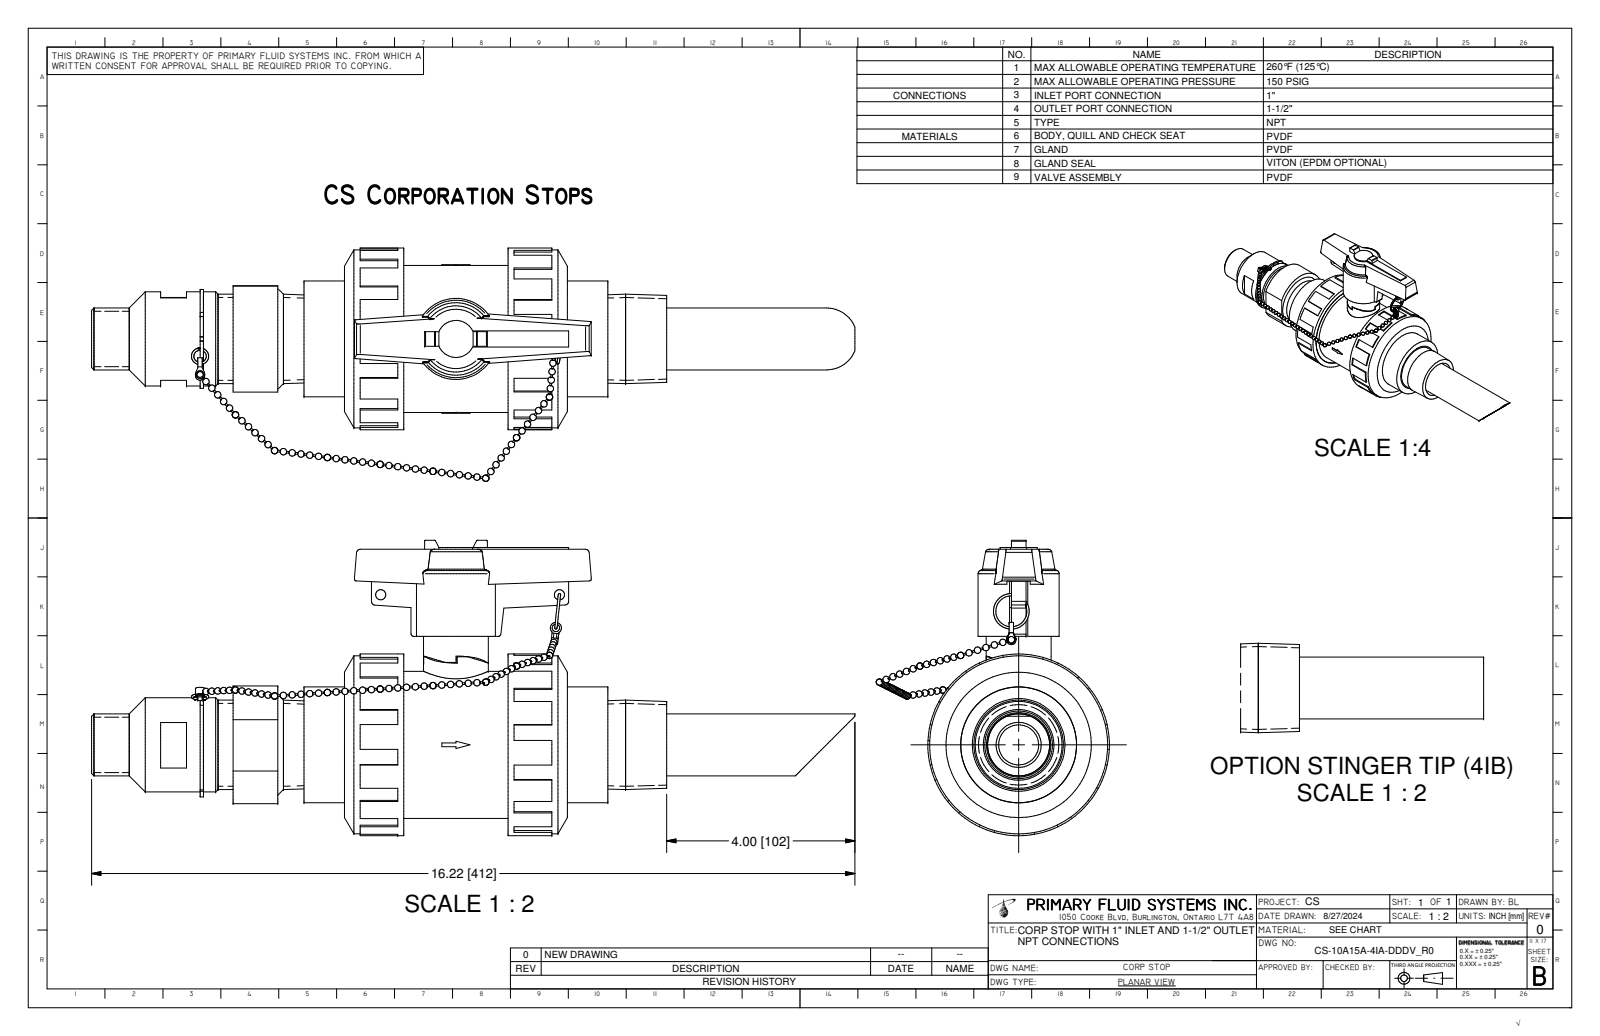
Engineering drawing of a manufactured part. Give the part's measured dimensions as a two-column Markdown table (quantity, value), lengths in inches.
| quantity | value |
| --- | --- |
| STEP written by | Autodesk Inventor 2025 (CONFIG_CONTROL_DESIGN) |
| units | inches |
| bodies | 19 solids, 534 faces (302 planar, 134 cylindrical, 98 other) |
| overall size | 16.221 × 6.274 × 4.956 |
| volume | 63.67 in³ |
| surface area | 403.6 in² |
| round holes (diameter × count) | 0.098 × 2, 0.15 × 2, 0.157 × 2, 0.217 × 2, 0.85 × 1, 0.957 × 1, 1.367 × 1, 1.5 × 1, 1.575 × 1, 1.803 × 1, 1.9 × 1, 1.969 × 1 |
| round bosses / shafts (diameter × count) | 0.035 × 9, 0.236 × 2, 3.858 × 1, 3.781 × 1, 3.472 × 1, 3.124 × 1, 2.46 × 1, 2 × 1 |
| partial cylindrical surfaces (radius × count) | 0.02 × 4, 0.079 × 4, 0.039 × 2, 0.049 × 2, 0.059 × 2, 0.098 × 2, 0.197 × 2, 0.394 × 1 |
| main face-to-face distances | 3.219, 1, 3.219, 4.219, 1, 0.259, 0.26, 1.26, 3.479, 4.479 |
| hole center spacings | 1.003, 0.314, 0.433, 0.708, 0.741, 1.182, 3.789, 3.798 |
